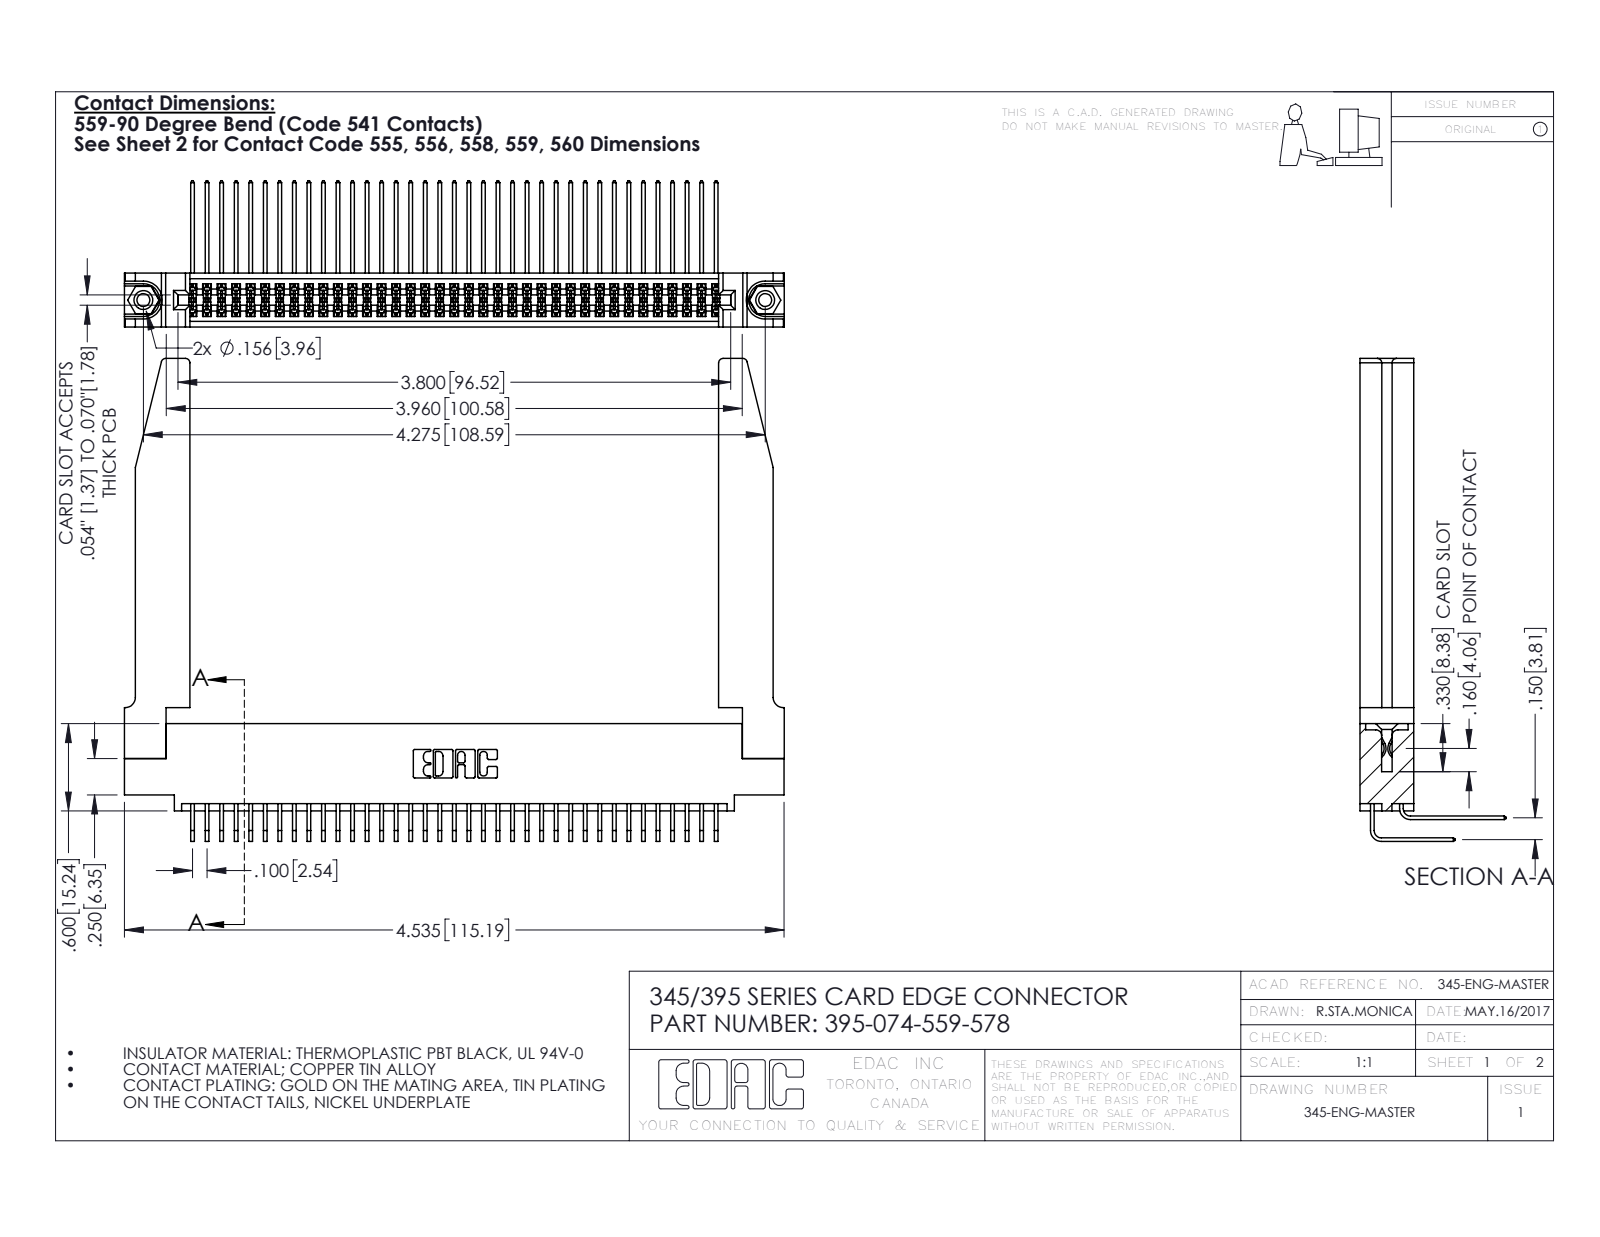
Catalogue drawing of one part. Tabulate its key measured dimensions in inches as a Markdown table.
| quantity | value |
| --- | --- |
| part name | 345-292-001_559 Tail - 2; 345-220-078_345-220-078; 345 Part_0.110 Offset - 0.156 Dia-TH; 345-250-001_345-250-001-102 (+2 more) |
| STEP written by | SolidWorks 2016 (CONFIG_CONTROL_DESIGN) |
| units | inches |
| bodies | 79 solids, 4212 faces (2816 planar, 1344 cylindrical, 52 other) |
| overall size | 4.536 × 3.319 × 1.005 |
| volume | 1.176 in³ |
| surface area | 40.05 in² |
| round holes (diameter × count) | 0.089 × 2, 0.125 × 2, 0.156 × 2, 0.064 × 1 |
| round bosses / shafts (diameter × count) | 0.155 × 2 |
| partial cylindrical surfaces (radius × count) | 0.006 × 111, 0.01 × 22, 0.03 × 8, 0.007 × 6, 0.031 × 6, 0.026 × 3, 0.014 × 2, 0.019 × 2 |
| main face-to-face distances | 0.37, 0.072, 0.298, 0.098, 0.272, 0.025, 0.2, 0.225, 0.175, 0.15 |
| hole center spacings | 0.27, 4.039, 4.275 |
